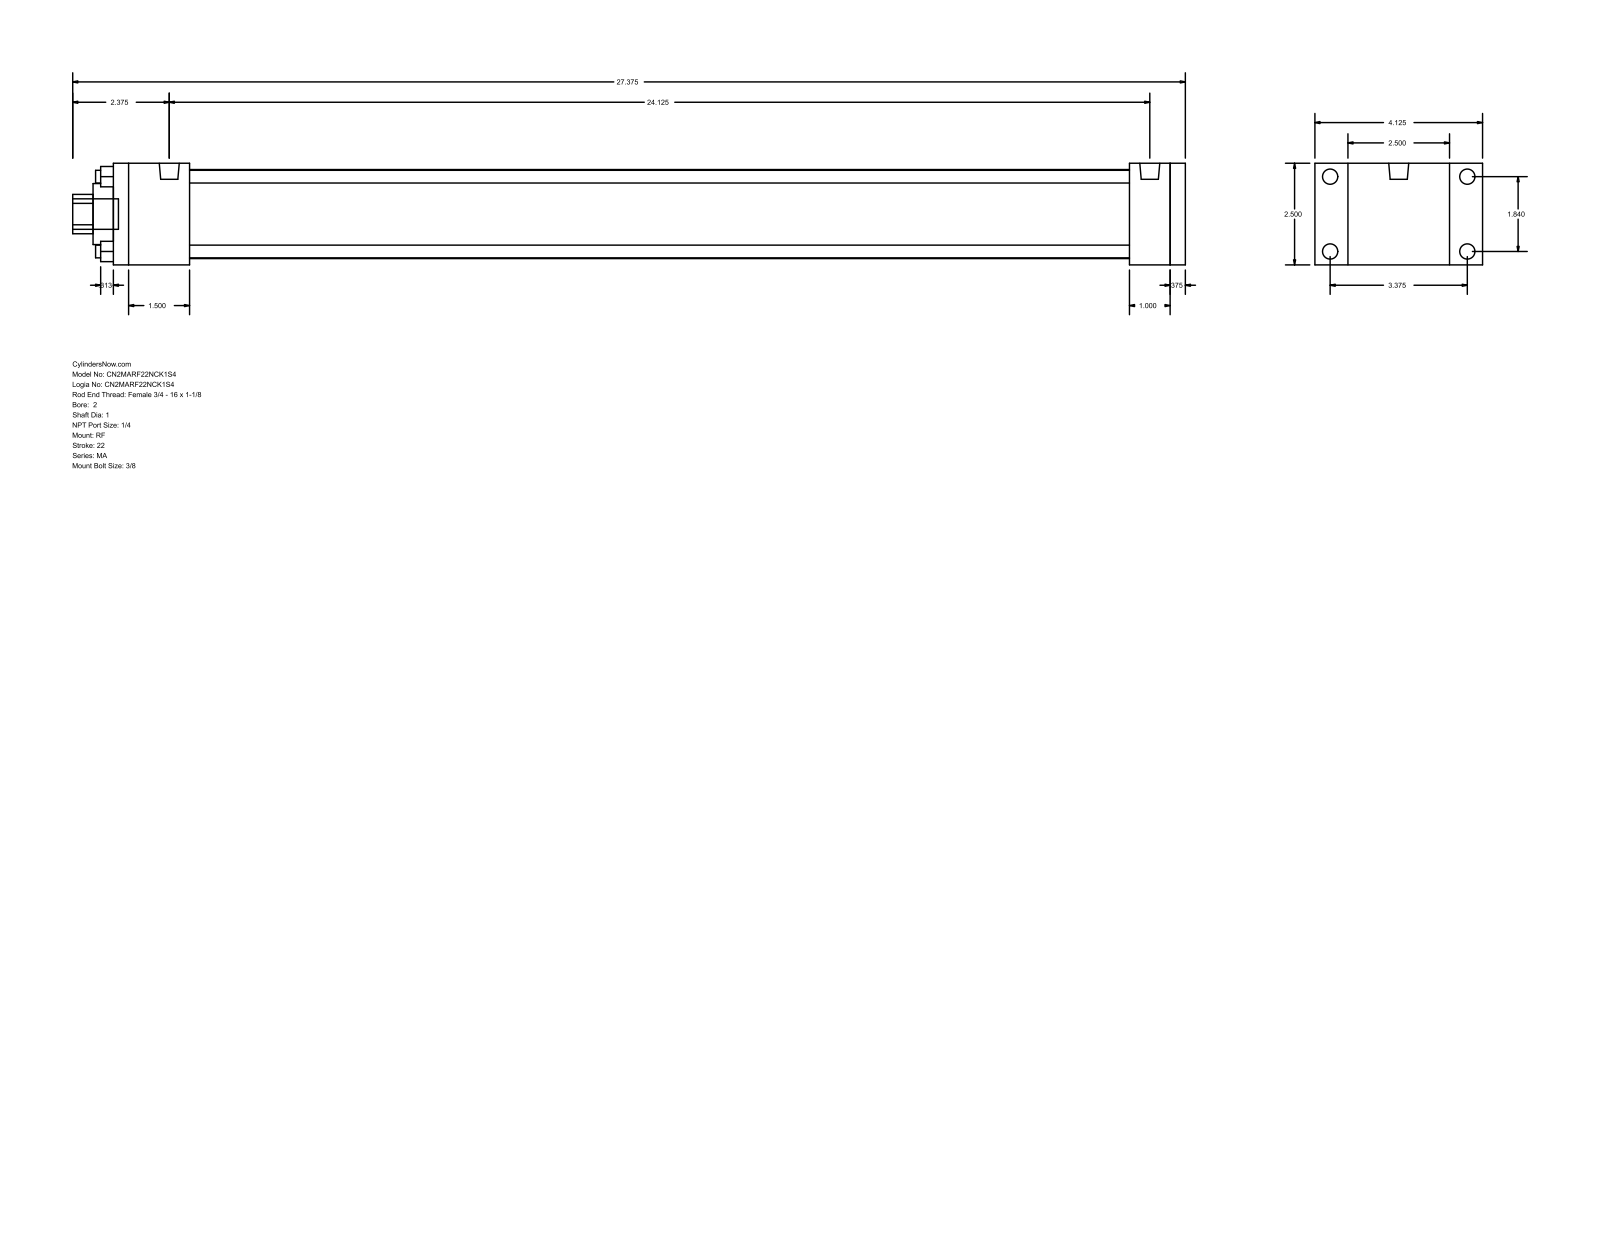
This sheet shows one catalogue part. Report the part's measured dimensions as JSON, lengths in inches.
{"part_name": "MA_RF__0200_1", "step_written_by": "GSSL Pune (CONFIG_CONTROL_DESIGN)", "units": "inches", "bodies": {"solids": 0, "faces": 92, "planar": 64, "cylindrical": 28, "other": 0}, "overall_size": [27.375, 4.125, 2.5], "round_holes": [[0.313, 4], [1, 1], [1.5, 1], [2.19, 1]], "round_bosses_or_shafts": [[0.375, 4], [0.313, 4], [0.492, 2], [0.75, 1]], "partial_cylinders_radius": [[0.484, 1]], "face_to_face_distances": [2.5, 26, 0.375, 26.375, 1, 0.813, 0.5, 1.875, 24.125, 24.5], "hole_center_spacings": [1.301, 1.84, 2.602]}
